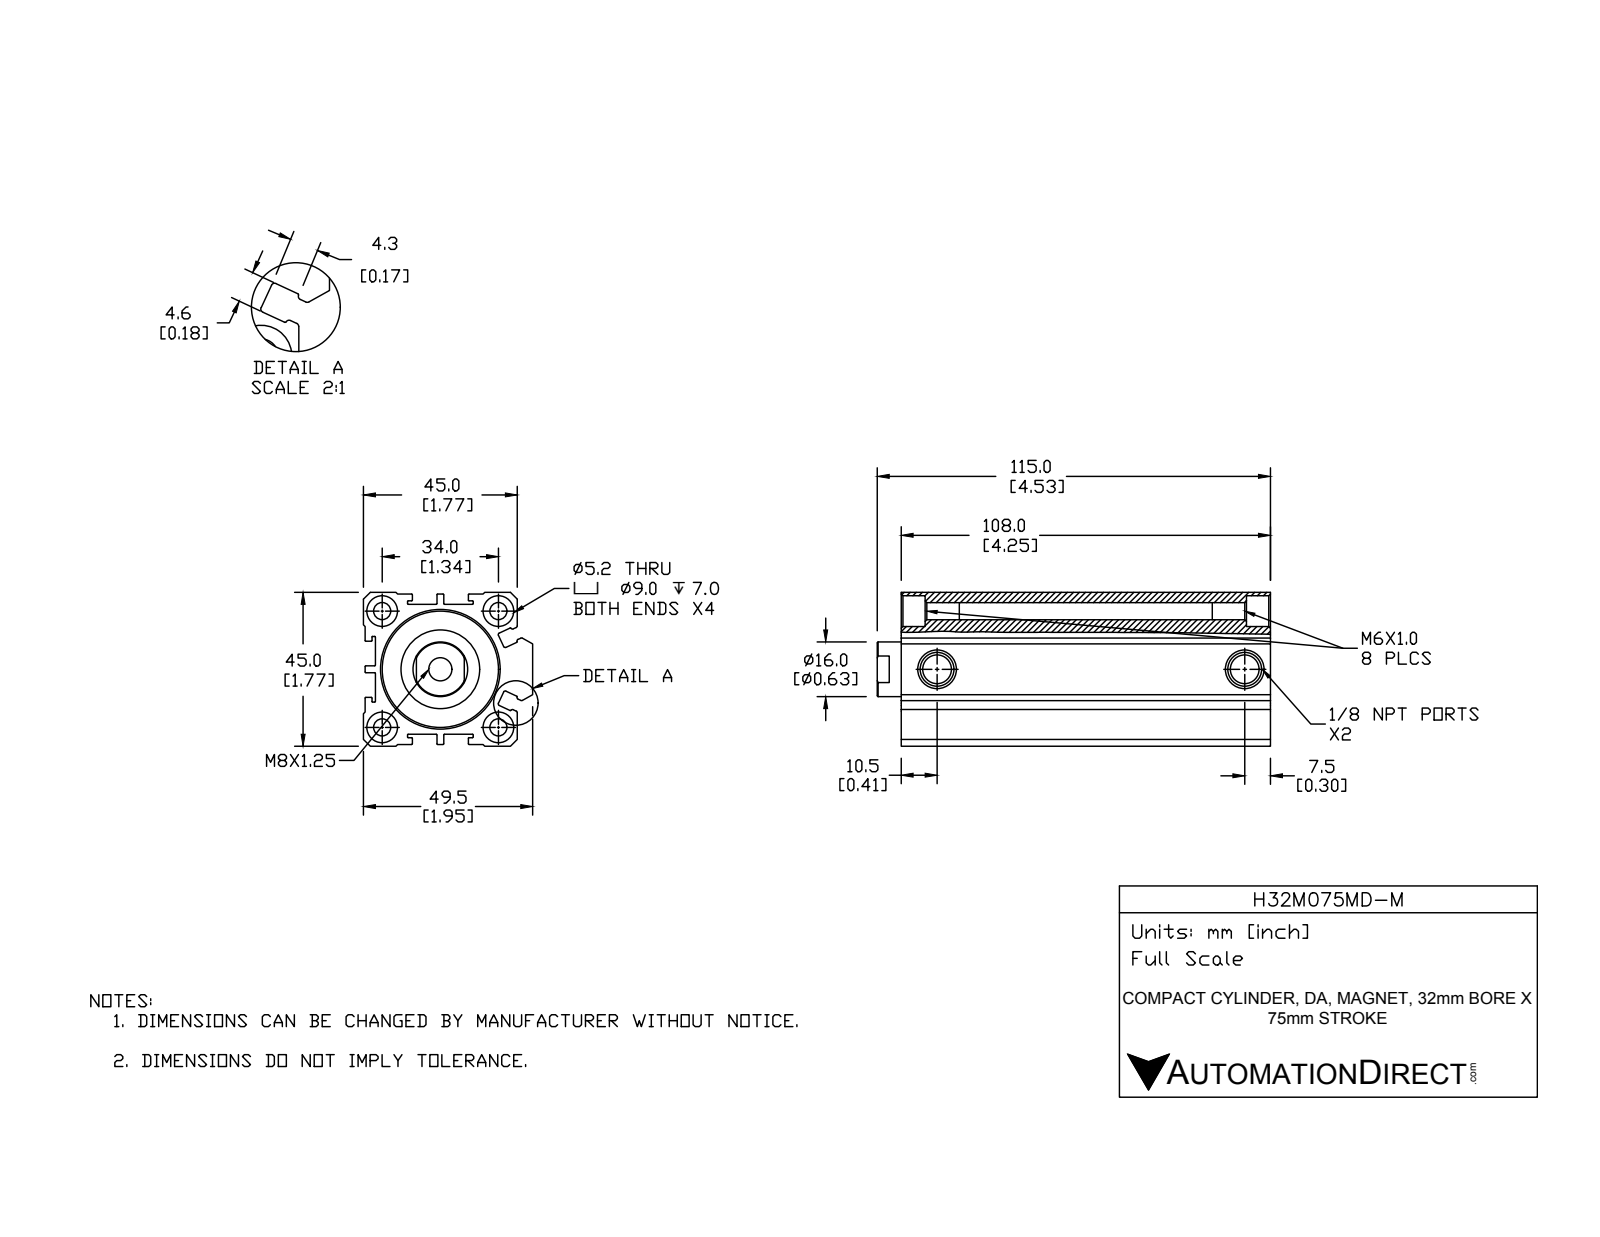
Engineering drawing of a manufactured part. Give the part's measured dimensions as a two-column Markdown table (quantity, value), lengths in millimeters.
| quantity | value |
| --- | --- |
| part name | H32M075MD-M-PISTON; H32M075MD-M-BODY; H32M075MD-M |
| STEP written by | SolidWorks 2015 (CONFIG_CONTROL_DESIGN) |
| units | millimeters |
| bodies | 2 solids, 255 faces (99 planar, 103 cylindrical, 53 other) |
| overall size | 115 × 49.5 × 45 |
| volume | 142 179 mm³ |
| surface area | 59 295 mm² |
| round holes (diameter × count) | 5 × 4, 9 × 4, 8.43 × 2, 6.8 × 1, 16 × 1, 23 × 1, 28 × 1, 32 × 1, 34 × 1 |
| round bosses / shafts (diameter × count) | 20 × 1 |
| partial cylindrical surfaces (radius × count) | 0.2 × 40, 0.5 × 12 |
| main face-to-face distances | 3.5, 41.5, 3, 45, 44.5, 0.5, 4.5, 41, 38, 21 |
| hole center spacings | 24.04, 34, 48.08, 90 |
